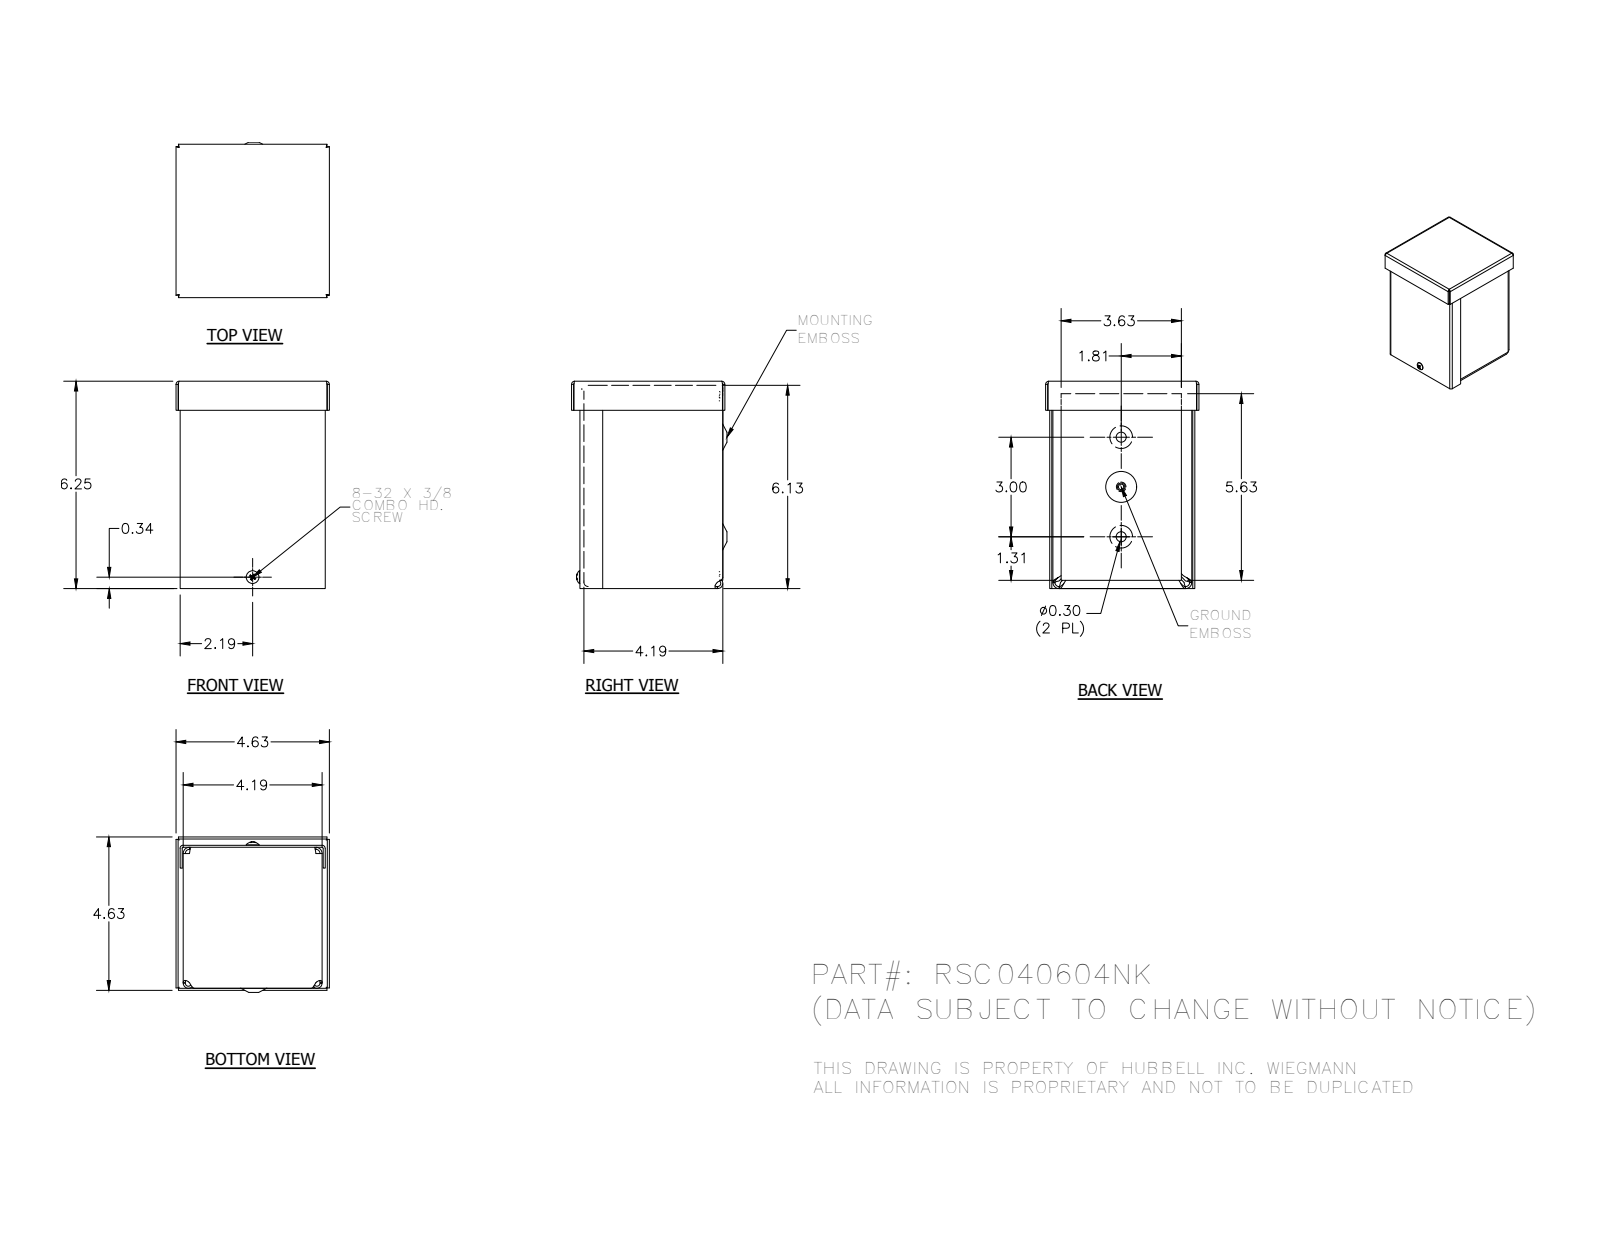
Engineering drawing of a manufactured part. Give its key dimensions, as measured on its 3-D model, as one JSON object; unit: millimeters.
{"part_name": "RSC040604NK_WRAP; RSC0406NK_LID; RSC0404NK_CAP; RSC0604NK_BKP (+2 more)", "step_written_by": "Autodesk Inventor 2014 (AUTOMOTIVE_DESIGN)", "units": "millimeters", "bodies": {"solids": 5, "faces": 303, "planar": 128, "cylindrical": 62, "other": 113}, "overall_size": [158.76, 119.09, 117.47], "volume_mm3": 203067, "surface_area_mm2": 263172, "round_holes": [[7.62, 2], [7.95, 2], [3.76, 1], [4.19, 1]], "round_bosses_or_shafts": [[9.75, 1], [5.8, 1], [4.17, 1]], "partial_cylinders_radius": [[3.17, 8], [4.75, 8], [0.79, 6], [2.37, 6], [1.4, 4], [1.57, 4], [2.38, 4], [2.97, 4]], "face_to_face_distances": [1.58, 1.57, 104.79, 107.93, 106.37, 103.21, 155.59, 3.15, 106.35, 1.59], "hole_center_spacings": [38.1, 27.76, 30.99, 65.85, 69.08, 76.2, 103.95, 107.18]}
